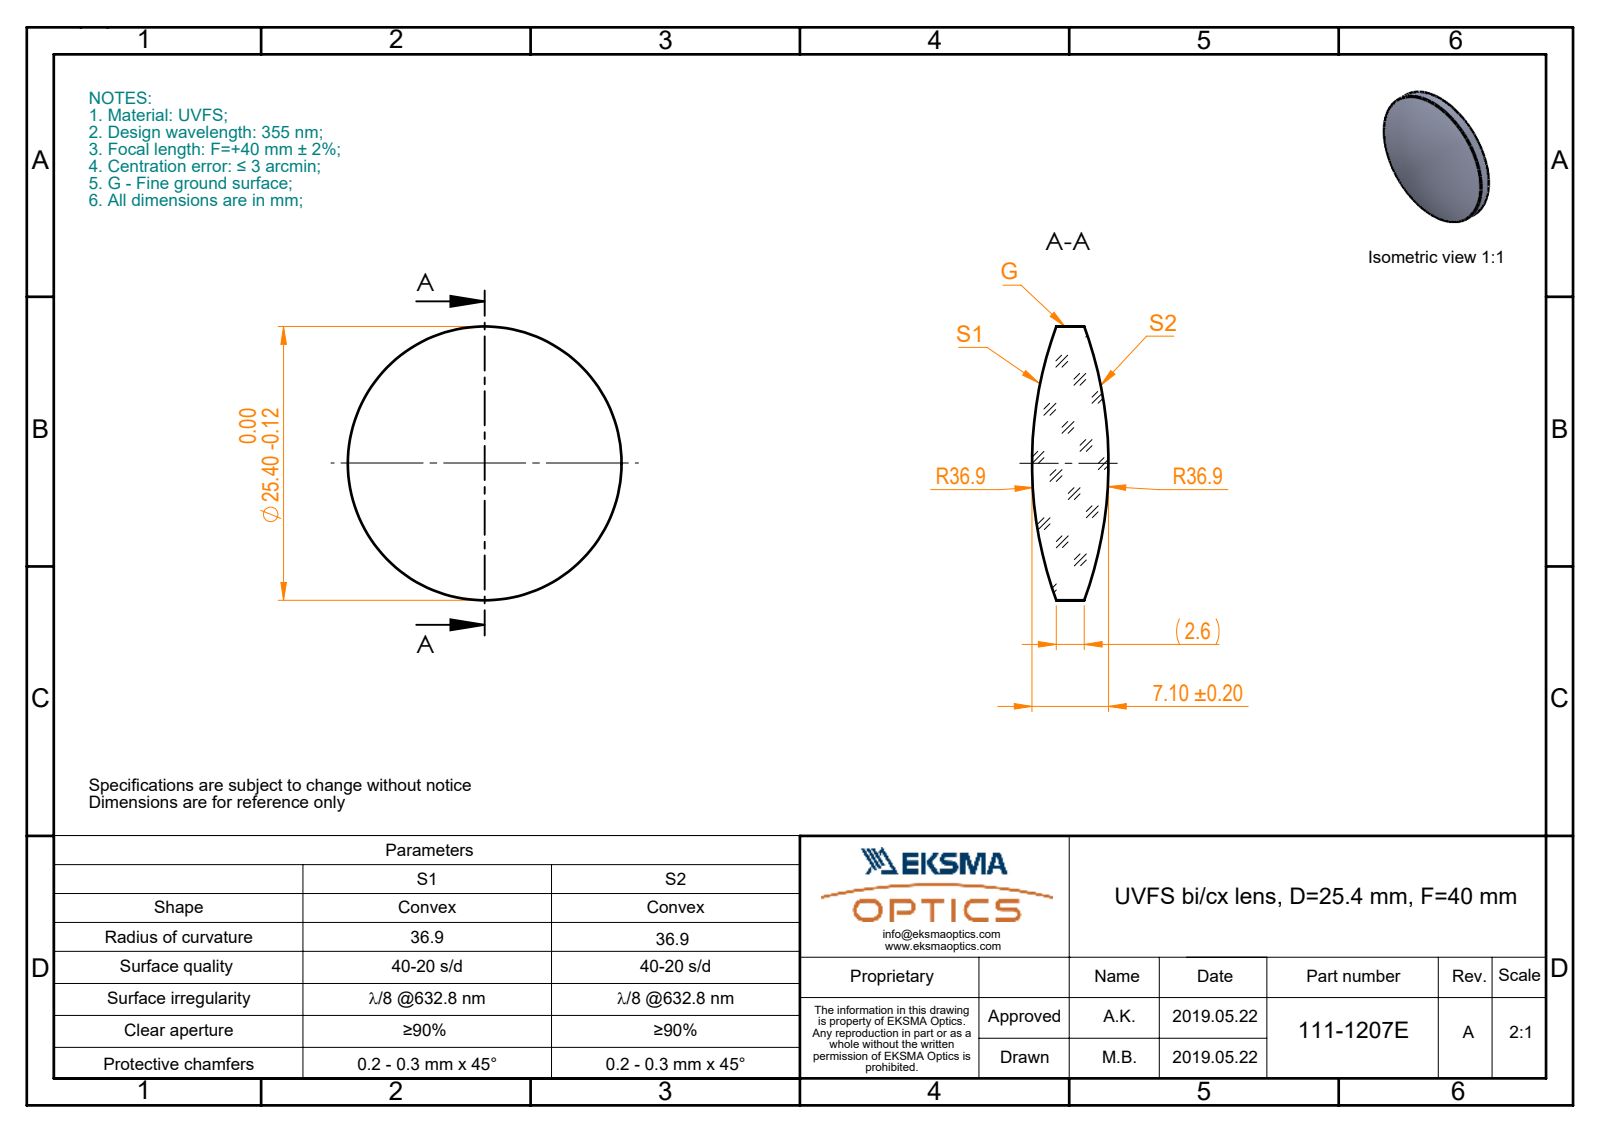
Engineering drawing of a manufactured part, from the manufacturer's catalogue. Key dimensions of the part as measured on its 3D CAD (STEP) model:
Part name (STEP PRODUCT): 111-1207E UVFS bi-cx 25.4 F40
STEP written by: SolidWorks 2017 (CONFIG_CONTROL_DESIGN)
Units: millimetres
Bodies: 1 solid, 6 faces (0 planar, 2 cylindrical, 4 other)
Overall size (bounding box): 25.4 × 25.4 × 7.1
Volume: 2 467 mm³ · Surface area: 1 252 mm²
Round bosses / shafts (diameter × count): ⌀25.4 ×1
